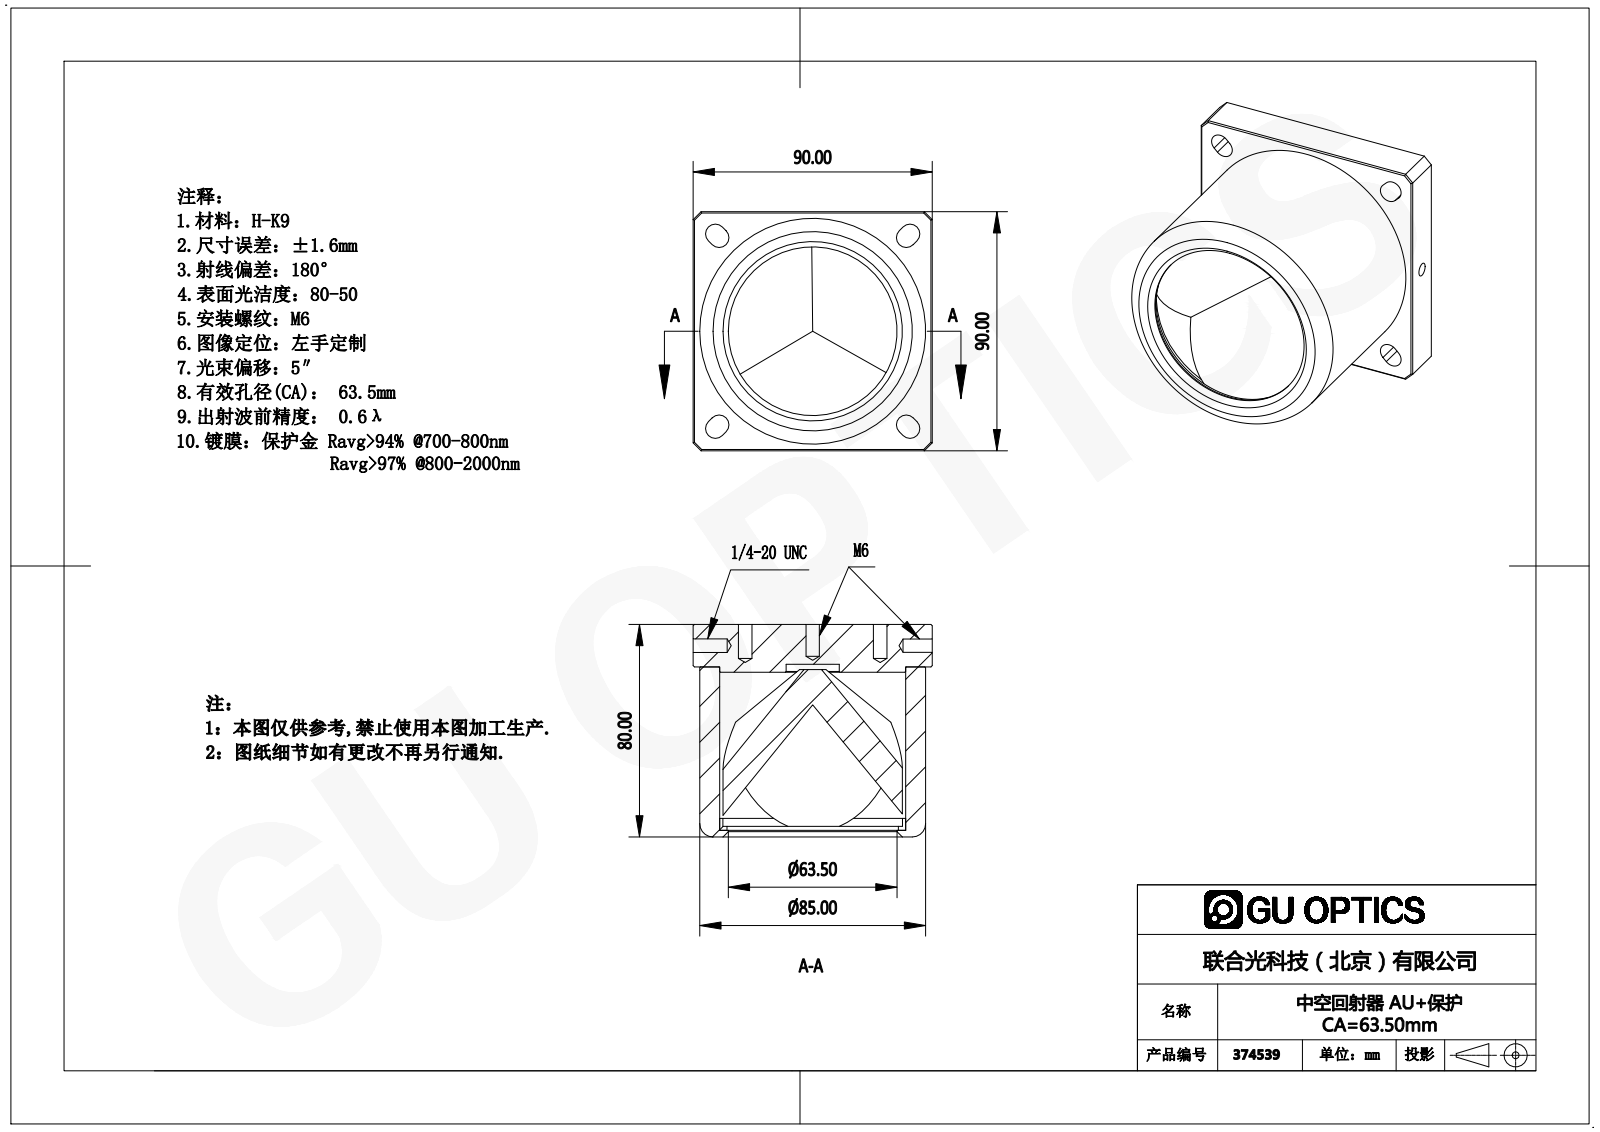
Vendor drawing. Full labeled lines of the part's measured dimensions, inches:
Part name (STEP PRODUCT): 374532
STEP written by: SolidWorks 2016 (AUTOMOTIVE_DESIGN)
Units: inches
Bodies: 8 solids, 274 faces (116 planar, 92 cylindrical, 66 other)
Overall size (bounding box): 3.543 × 3.543 × 3.15
Volume: 18.82 in³ · Surface area: 128.3 in²
Round holes (diameter × count): ⌀0.197 ×6, ⌀0.201 ×5, ⌀0.13 ×4, ⌀0.177 ×4, ⌀0.295 ×4, ⌀0.787 ×1, ⌀2.5 ×1, ⌀2.539 ×1, ⌀2.661 ×1
Round bosses / shafts (diameter × count): ⌀0.276 ×4, ⌀0.157 ×4, ⌀3.346 ×1, ⌀2.756 ×1, ⌀2.657 ×1
Partial cylindrical surfaces — rounded edges, fillets, slot ends (radius × count): R0.146 ×8
Main face-to-face distances: 0.394, 0.63, 0.079, 0.709, 3.543, 3.051, 2.421, 2.343, 2.52, 3.15
Hole centre spacings: 0.765, 1, 1.081, 1.414, 1.824, 1.848, 2.342, 0.526
